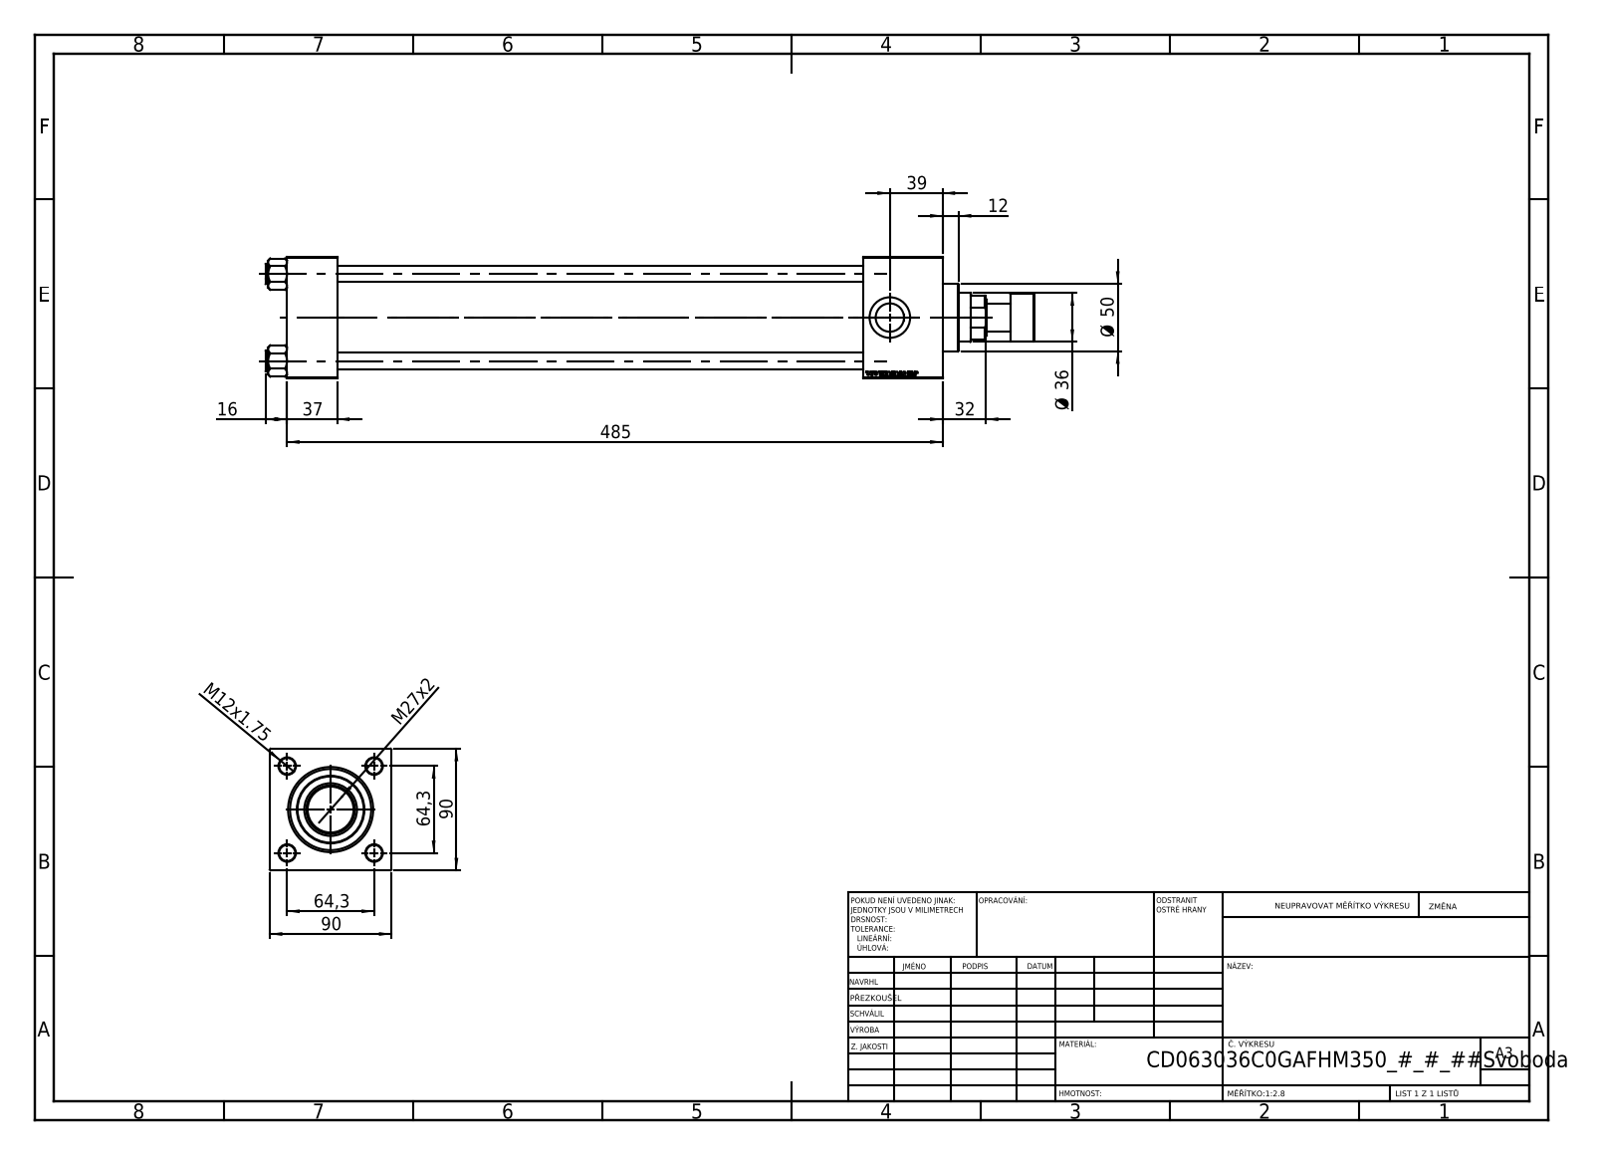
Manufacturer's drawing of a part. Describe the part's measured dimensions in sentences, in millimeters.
The part is named "V215CD_VC_C; V215CD_Body_C; V215CD_C_TYCINKA; NUT_M5_V215CD_C (+2 more)". Its 3-D file was written by "SolidWorks 2019 (CONFIG_CONTROL_DESIGN)". It is 12 solids with 1163 faces: 530 planar, 91 cylindrical and 542 other. Overall it measures 569 by 90 by 90 millimeters. Its volume is 1 682 000 cubic millimeters and its surface area 413 738 square millimeters. Round holes: 4 of diameter 12, 2 of diameter 7, 2 of diameter 20.96, 2 of diameter 30, 1 of diameter 25.5, 1 of diameter 36, 1 of diameter 39, 1 of diameter 50, 1 of diameter 60, 1 of diameter 63. Round bosses or shafts: 4 of diameter 15, 1 of diameter 69, 1 of diameter 35, 1 of diameter 21. The main face-to-face distances are 90, 37, 485, 448, 59, 426, 389, 456.3, 419.3, 30.3. The hole center spacings are 45.47, 64.3, 90.93.
